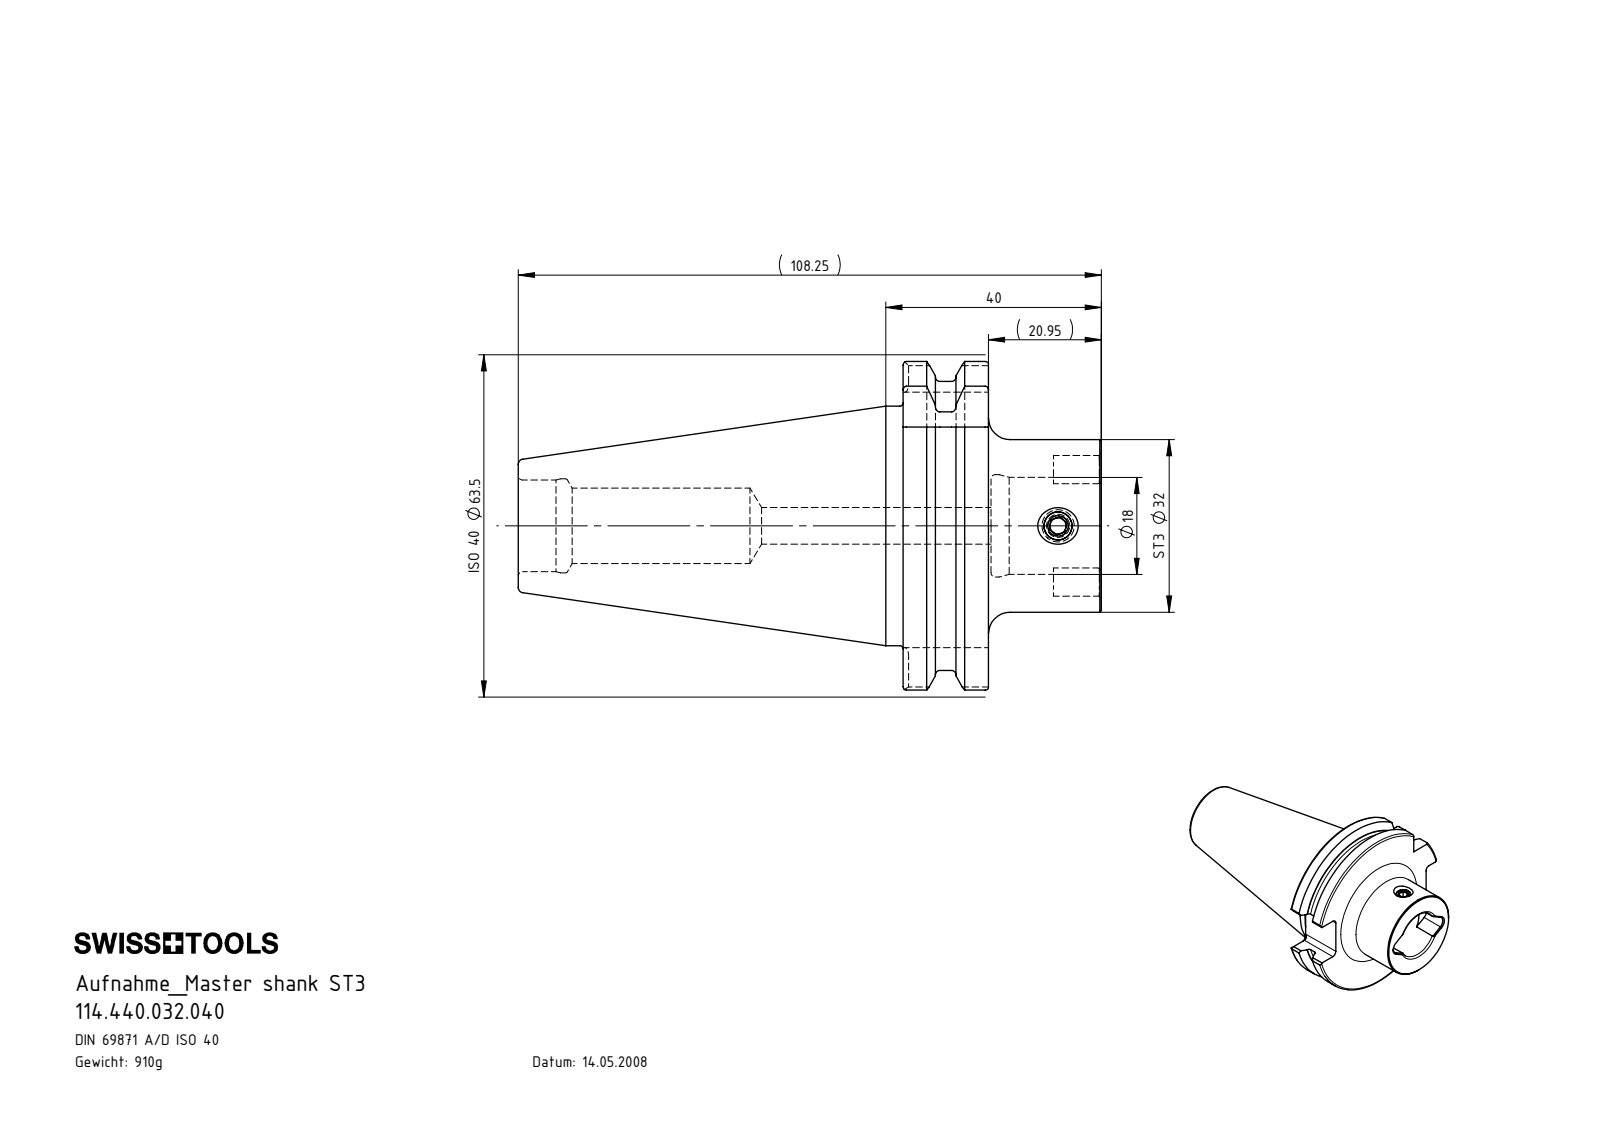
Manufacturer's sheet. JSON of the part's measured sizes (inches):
{"part_name": "ST3-ER1.001.008_A; SK4.ST3.K01.040; SK4-ST3.K01.040_B", "step_written_by": "SolidWorks 2017 (AUTOMOTIVE_DESIGN)", "units": "inches", "bodies": {"solids": 2, "faces": 126, "planar": 54, "cylindrical": 30, "other": 42}, "overall_size": [4.262, 2.5, 2.399], "volume_in3": 7.076, "surface_area_in2": 35.32, "round_holes": [[0.118, 1], [0.207, 1], [0.268, 1], [0.551, 1], [0.669, 1], [0.687, 1], [0.709, 1], [0.748, 1]], "round_bosses_or_shafts": [[1.75, 1], [1.26, 1], [0.236, 1]], "partial_cylinders_radius": [[0.063, 8], [0.098, 2], [1.102, 1], [1.25, 1]], "face_to_face_distances": [0.624, 1.449, 0.825, 1.866, 0.642, 0.018, 0.807, 2.813, 3.437, 3.455]}
